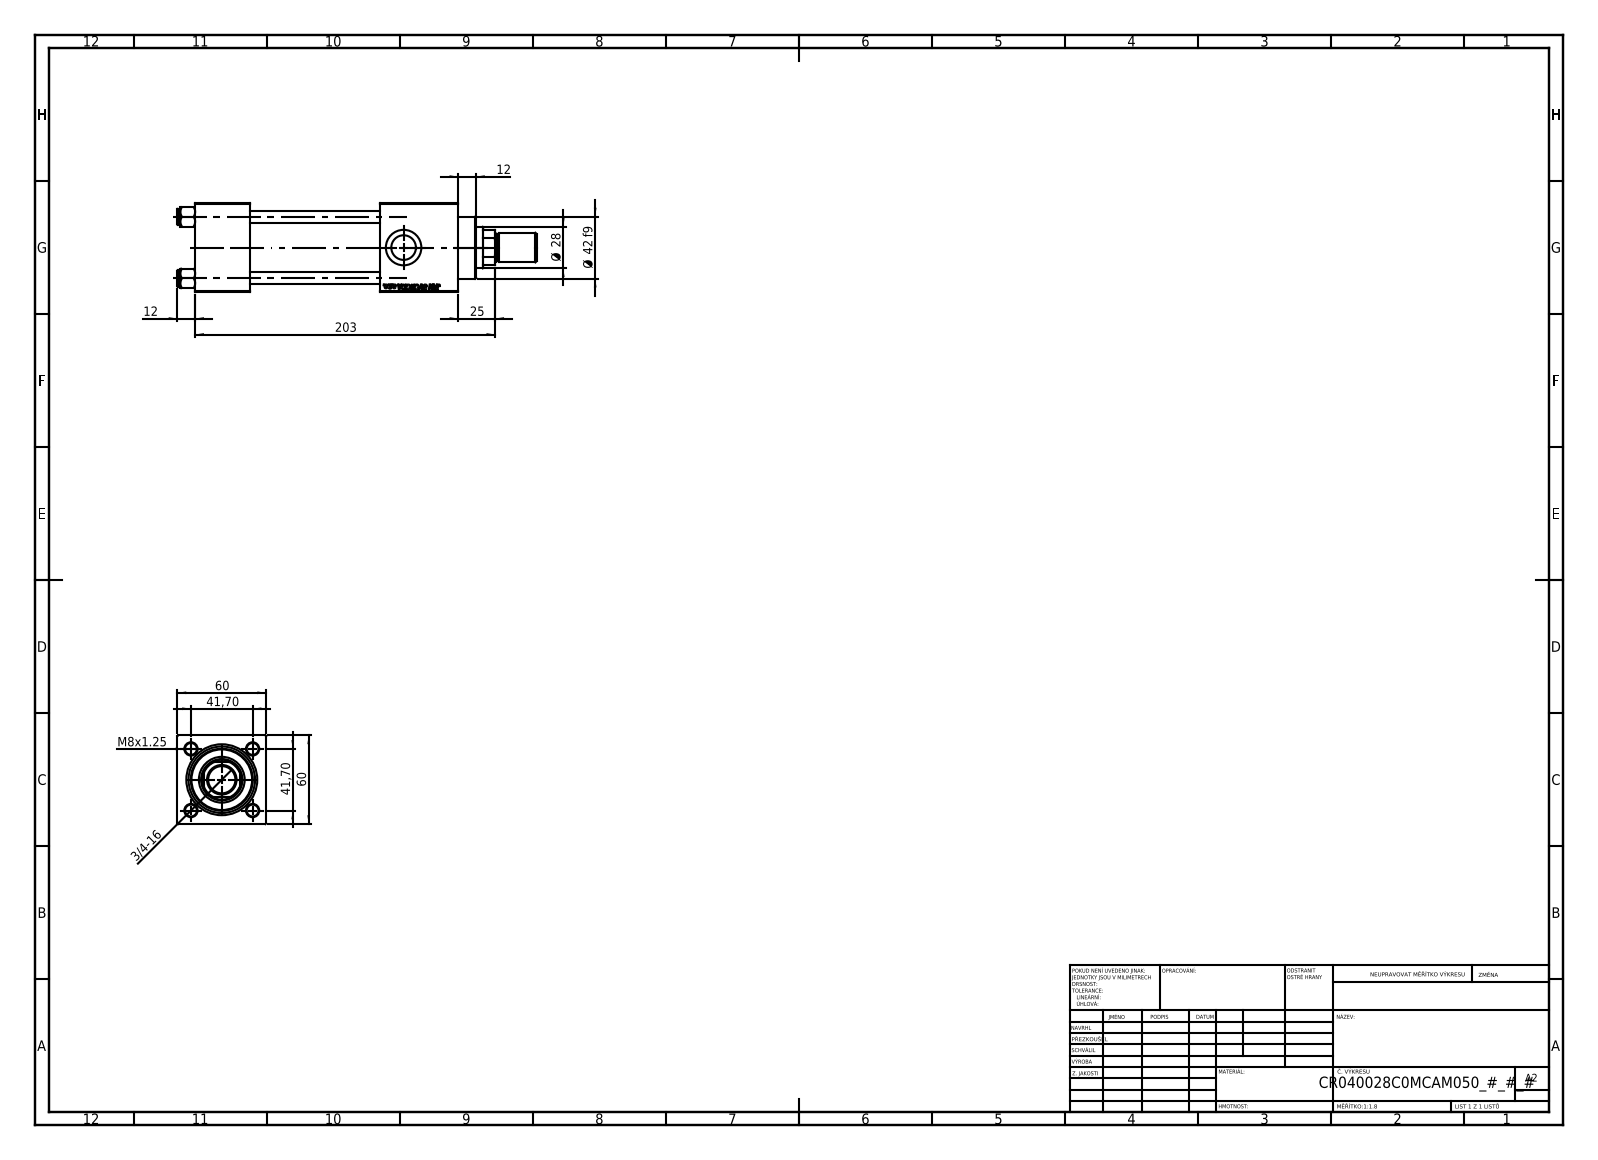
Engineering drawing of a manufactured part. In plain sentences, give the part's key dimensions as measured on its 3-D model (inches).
The part is named "V215CR_C_Body; NUT_M5_C; V215_VC_A; V215CR_VCP_C (+2 more)". Its 3-D file was written by "SolidWorks 2019 (CONFIG_CONTROL_DESIGN)". It is 12 solids with 1163 faces: 530 planar, 91 cylindrical and 542 other. Overall it measures 9.567 by 2.362 by 2.362 inches. Its volume is 28.65 cubic inches and its surface area 197.8 square inches. Round holes: 4 of diameter 0.315, 2 of diameter 0.276, 2 of diameter 0.656, 2 of diameter 0.945, 1 of diameter 0.728, 1 of diameter 1.102, 1 of diameter 1.22, 1 of diameter 1.575, 1 of diameter 1.772. Round bosses or shafts: 4 of diameter 0.433, 1 of diameter 1.811, 1 of diameter 1.654, 1 of diameter 0.787, 1 of diameter 0.709. Partial cylindrical surfaces (rounded edges, fillets, slot ends): 1 of radius 0.531. The main face-to-face distances are 2.362, 1.457, 4.921, 3.465, 2.087, 5.878, 4.421, 0.957, 7.008, 5.551. The hole center spacings are 1.161, 1.642, 2.322.
